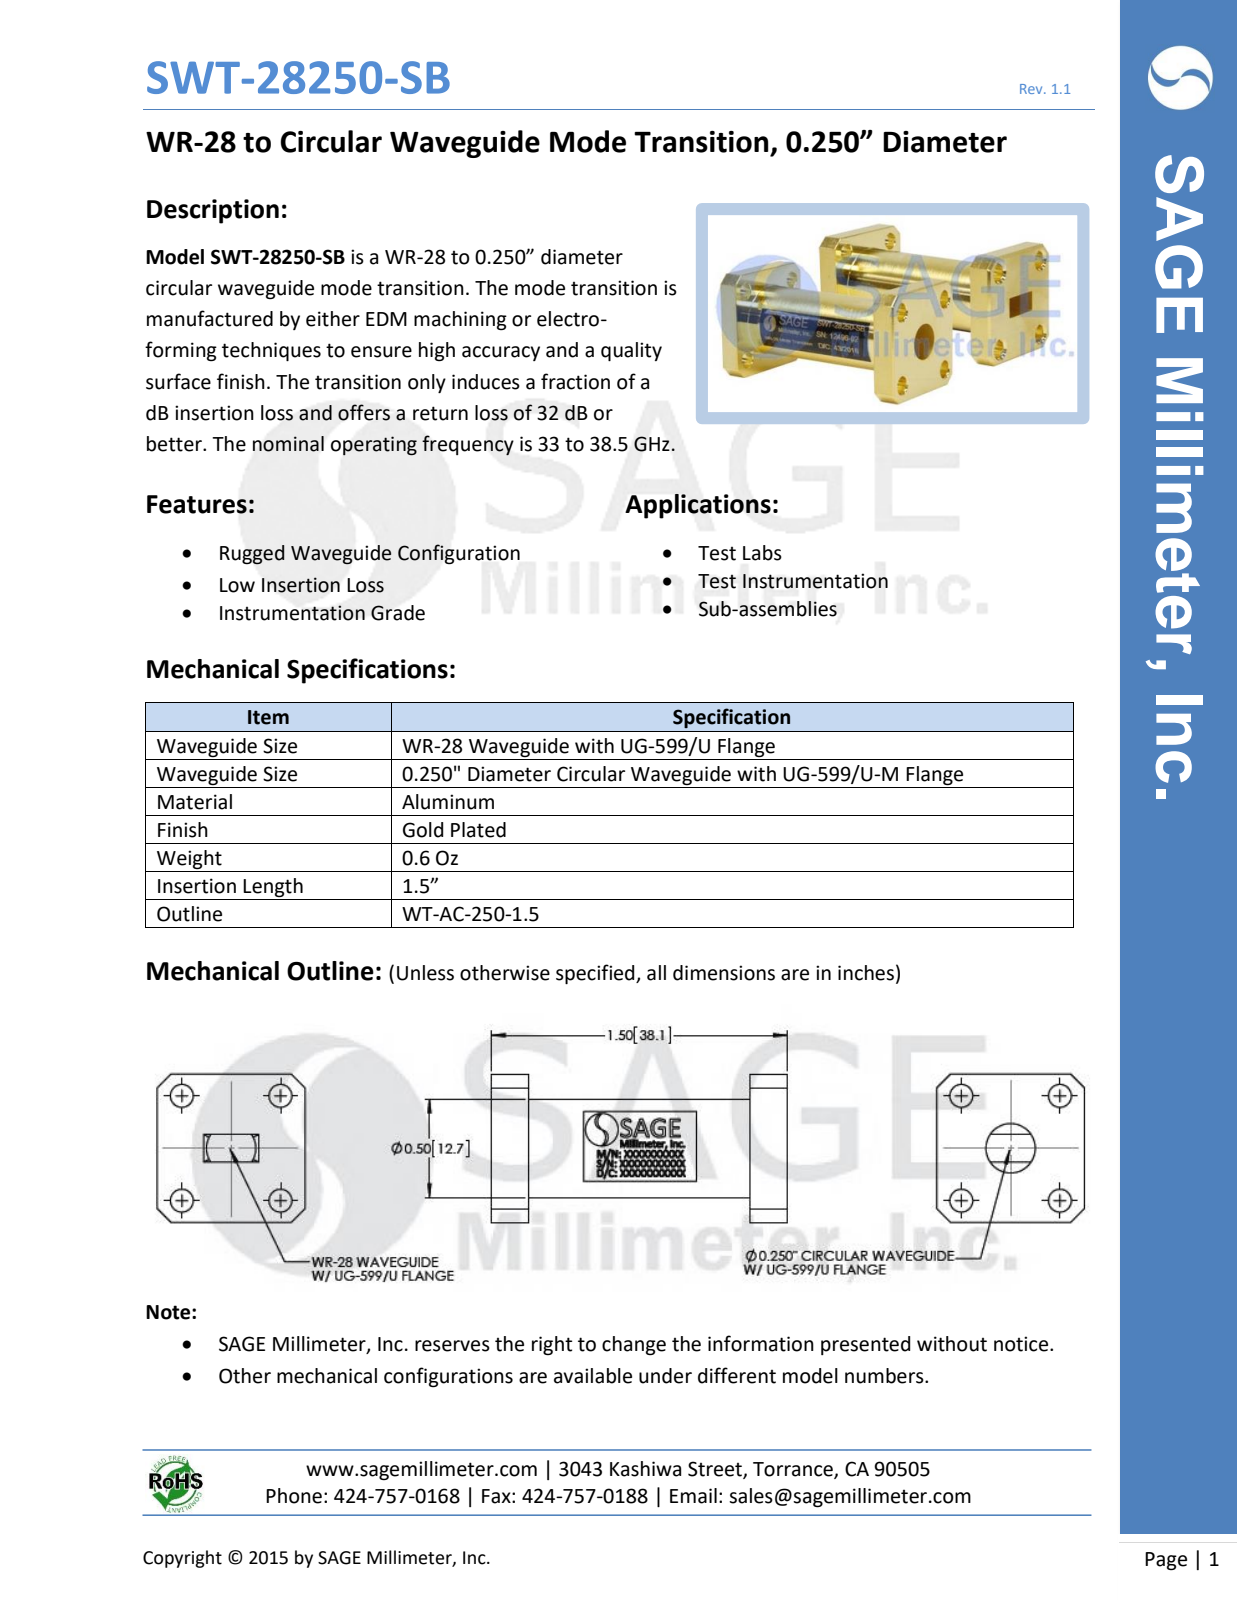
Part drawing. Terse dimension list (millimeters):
name: DMWT-28-321-C
written by: SolidWorks 2013 (CONFIG_CONTROL_DESIGN)
unit: mm
bodies: 1 solid, 42 faces (20 planar, 18 cylindrical, 4 other)
size: 50.8 × 19.1 × 19.1
volume: 6 960 mm³; area: 4 952 mm²
holes: 4× ⌀2.9
bosses: 1× ⌀13.5
face distances: 4.8, 46, 19.1, 50.8, 41.1, 24.4
hole spacings: 12.7, 13.5, 18.5
